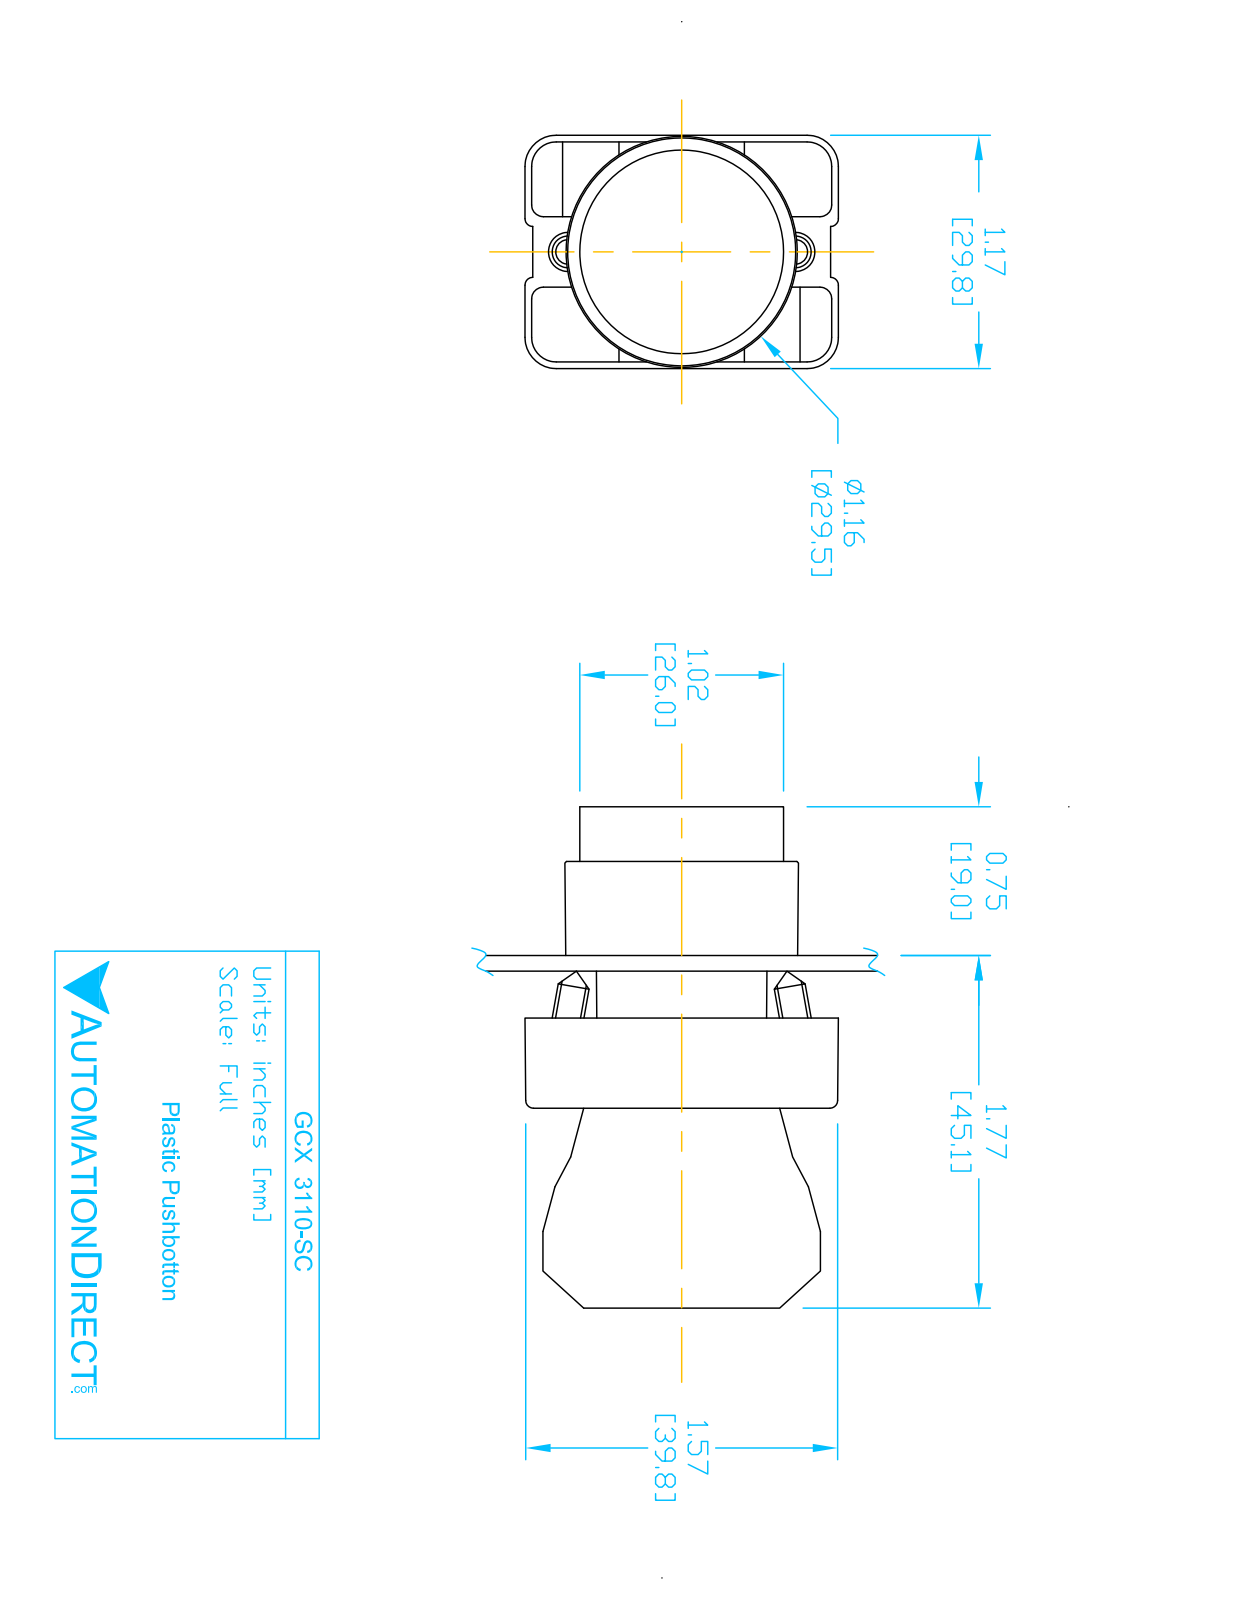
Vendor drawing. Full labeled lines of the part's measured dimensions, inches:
Part name (STEP PRODUCT): ECX3029-2; GCX3110 OPERATOR; GCX3110-SC
STEP written by: SolidWorks 2016 (AUTOMOTIVE_DESIGN)
Units: inches
Bodies: 5 solids, 290 faces (147 planar, 118 cylindrical, 25 other)
Overall size (bounding box): 1.683 × 1.581 × 1.177
Volume: 0.933 in³ · Surface area: 19.73 in²
Round holes (diameter × count): ⌀0.124 ×2, ⌀0.13 ×2, ⌀0.197 ×1, ⌀0.878 ×1, ⌀0.888 ×1, ⌀1.024 ×1
Round bosses / shafts (diameter × count): ⌀0.157 ×2, ⌀1.175 ×1, ⌀1.004 ×1, ⌀0.945 ×1, ⌀0.856 ×1, ⌀0.78 ×1
Partial cylindrical surfaces — rounded edges, fillets, slot ends (radius × count): R0.059 ×24, R0.041 ×12, R0.124 ×12, R0.157 ×12, R0.039 ×4, R0.128 ×2, R0.392 ×1, R0.398 ×1
Main face-to-face distances: 0.033, 1.193, 0.031, 0.72, 0.472, 0.689, 1.161, 1.469, 1.437, 0.748
